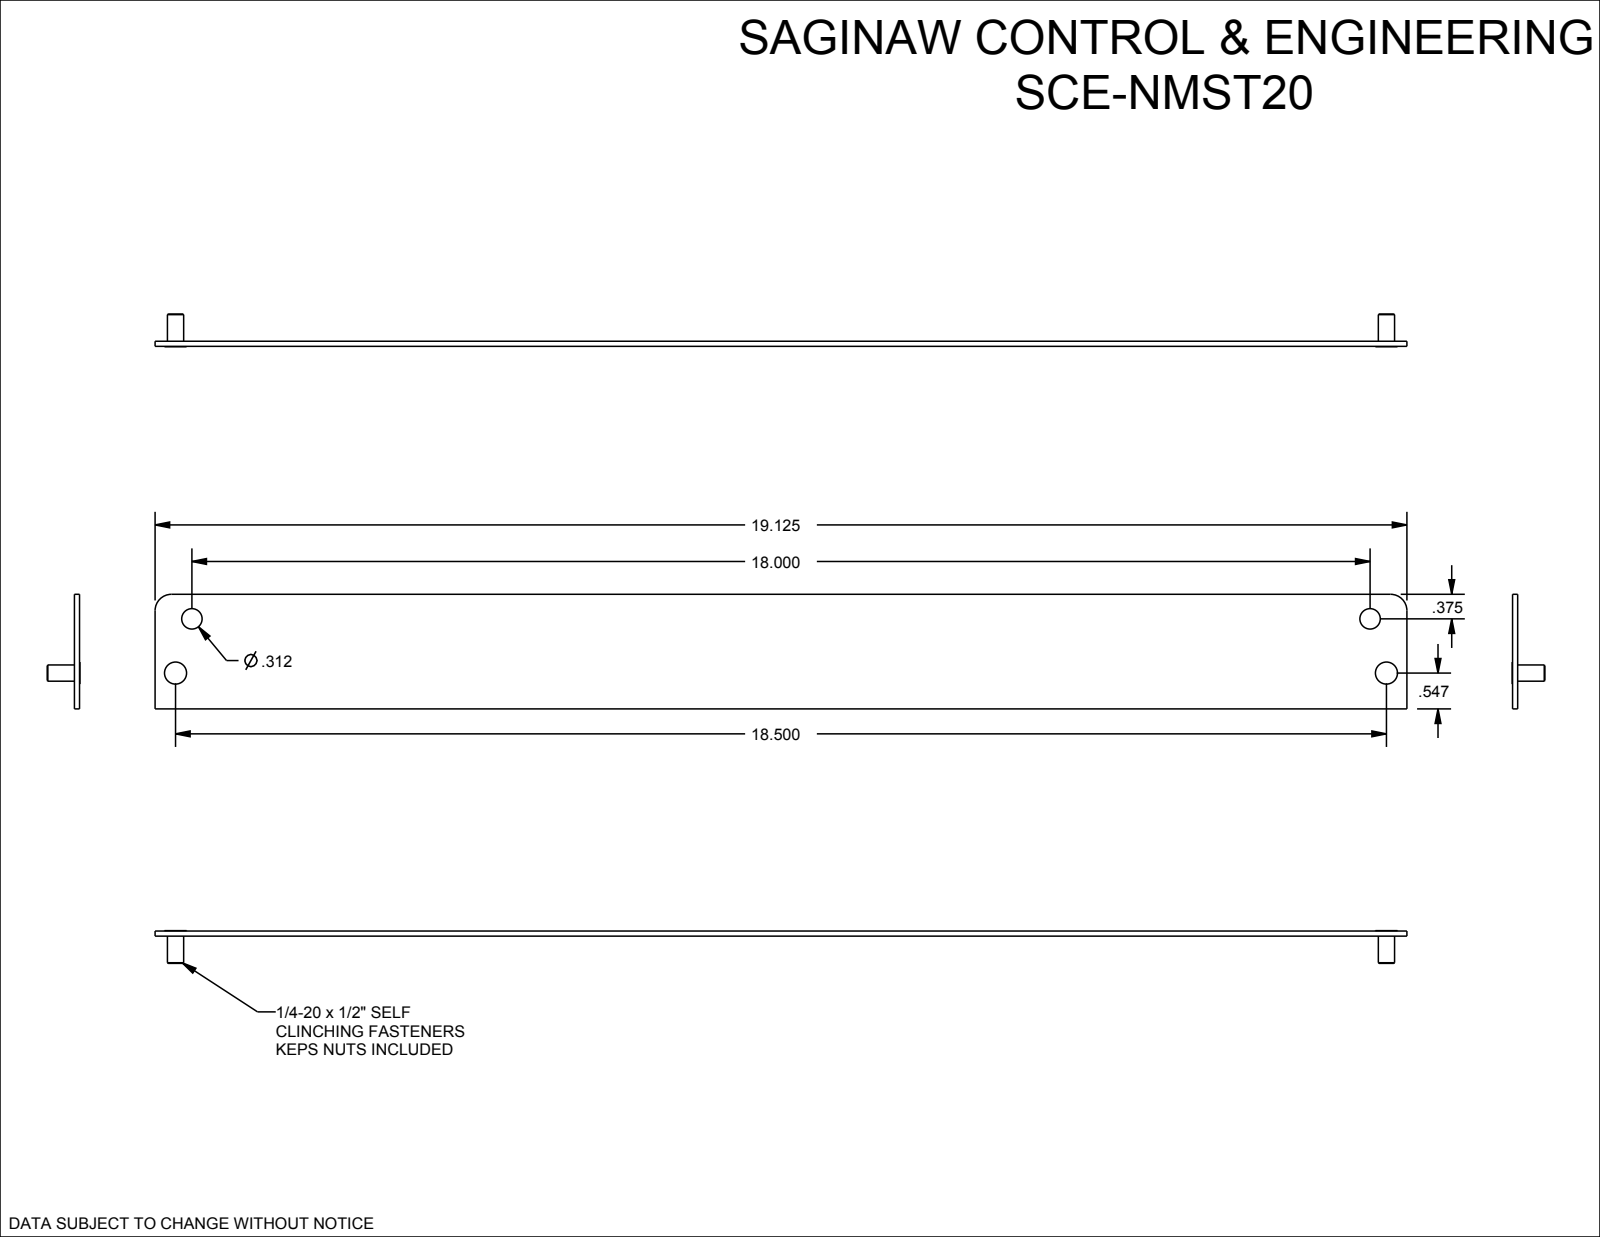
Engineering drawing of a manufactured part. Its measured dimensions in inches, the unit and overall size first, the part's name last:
Units: inches
Overall size (bounding box): 19.125 × 1.75 × 0.5
Round holes (diameter × count): ⌀0.25 ×2, ⌀0.312 ×2
Round bosses / shafts (diameter × count): ⌀0.337 ×2, ⌀0.248 ×2
Partial cylindrical surfaces — rounded edges, fillets, slot ends (radius × count): R0.25 ×2
Main face-to-face distances: 0.078, 1.75, 0.084, 19.125, 0.066, 0.018, 0.416, 0.482, 0.494, 0.5
Hole centre spacings: 0.865, 18.269, 18, 18.5
Volume: 2.639 in³ · Surface area: 71.03 in²
Bodies: 3 solids, 24 faces (12 planar, 10 cylindrical, 2 other)
Part name (STEP PRODUCT): SCE-NMST20
STEP written by: SolidWorks 2019 (AUTOMOTIVE_DESIGN)
